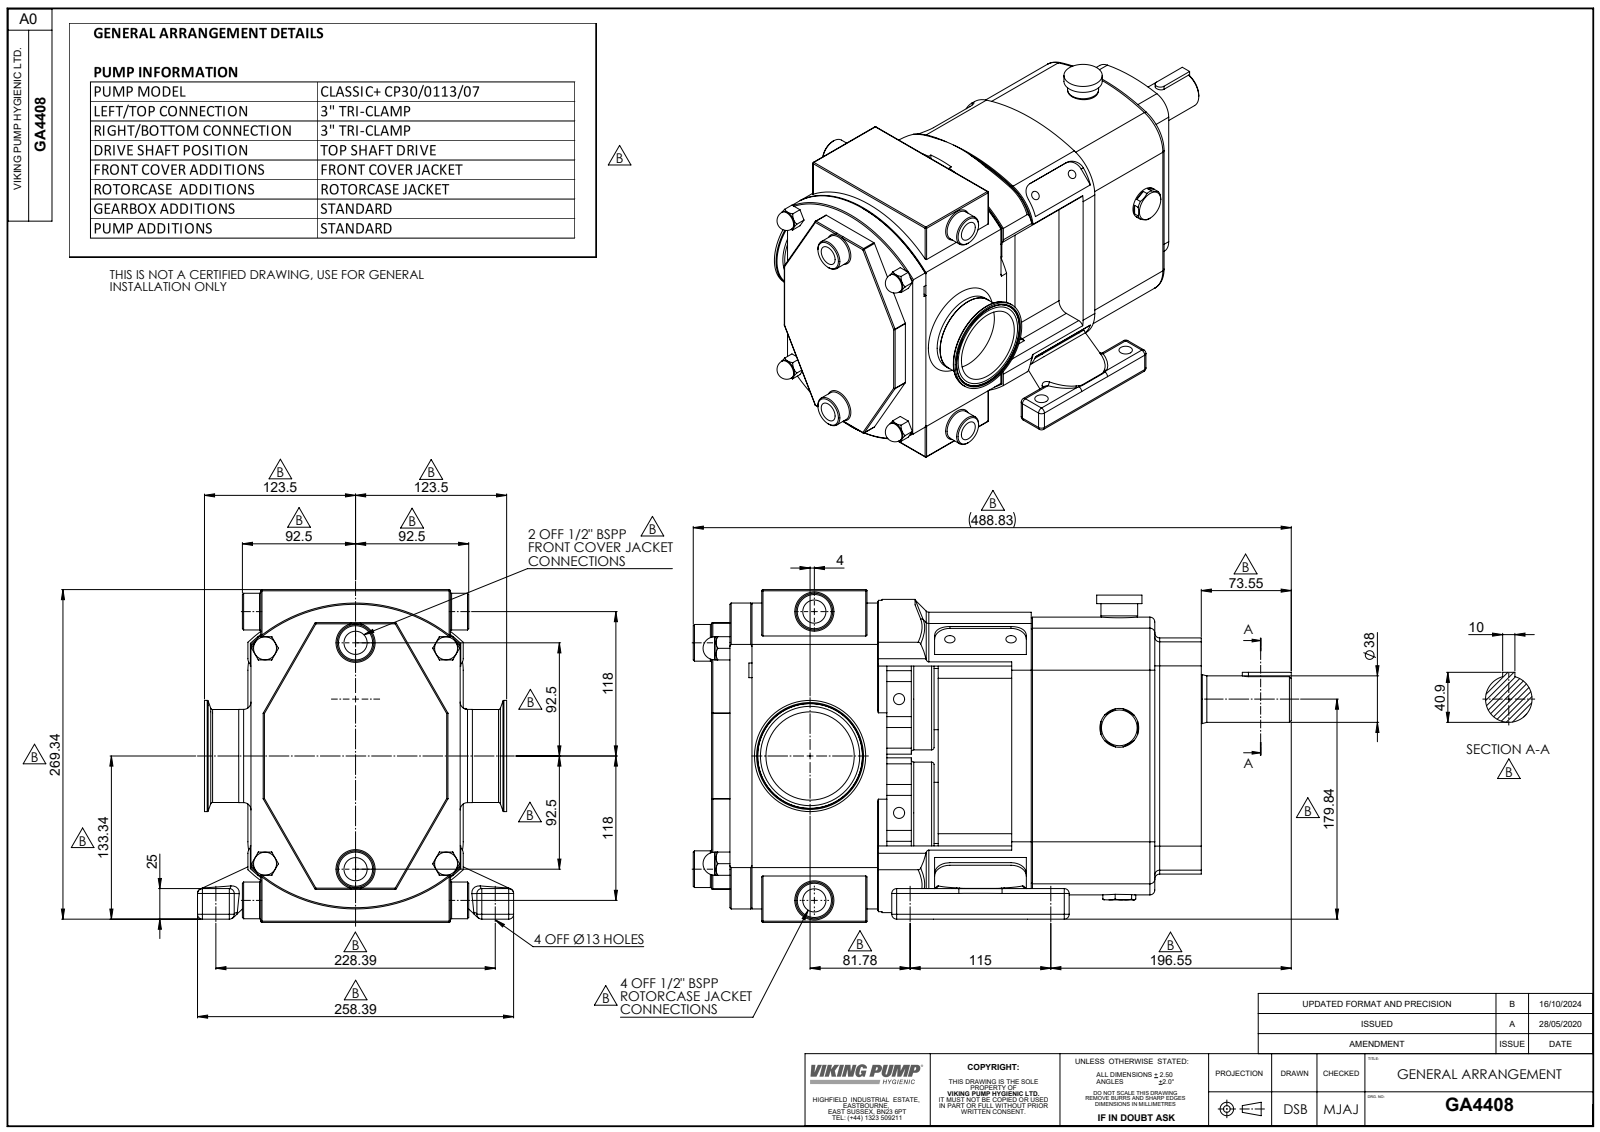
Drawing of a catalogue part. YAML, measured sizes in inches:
part_name: "Copy of CP30-0113-07 H T^GA4408; GA4408; Copy of MP30 Half Inch BSP Jacket^GA4408; Copy of Z94-5121-55 - 3 INCH^GA4408 (+1 more)"
step_written_by: "SolidWorks 2023 (AUTOMOTIVE_DESIGN)"
units: inches
bodies: {solids: 6, faces: 865, planar: 291, cylindrical: 297, other: 277}
overall_size: [19.245, 10.709, 10.172]
volume: 845.8
surface_area: 1118
round_holes:
  - {diameter: 0.335, count: 4}
  - {diameter: 0.398, count: 4}
  - {diameter: 0.512, count: 4}
  - {diameter: 0.747, count: 4}
  - {diameter: 0.358, count: 2}
  - {diameter: 1.378, count: 1}
  - {diameter: 2.843, count: 1}
round_bosses_or_shafts:
  - {diameter: 1.181, count: 5}
  - {diameter: 0.74, count: 4}
  - {diameter: 3.268, count: 2}
  - {diameter: 1.969, count: 2}
  - {diameter: 3.579, count: 1}
  - {diameter: 3, count: 1}
  - {diameter: 2.992, count: 1}
  - {diameter: 1.575, count: 1}
partial_cylinders:
  - {radius: 0.039, count: 44}
  - {radius: 0.157, count: 44}
  - {radius: 0.394, count: 12}
  - {radius: 0.236, count: 10}
  - {radius: 0.492, count: 4}
  - {radius: 0.495, count: 4}
  - {radius: 0.496, count: 4}
  - {radius: 0.787, count: 4}
face_to_face_distances: [0.059, 6.673, 0.591, 5.472, 1.496, 6.702, 7.293, 8.467, 15.169, 15.759]
hole_center_spacings: [2.506, 1.372, 1.97, 3.31, 3.399, 3.543, 3.919, 4.402]
